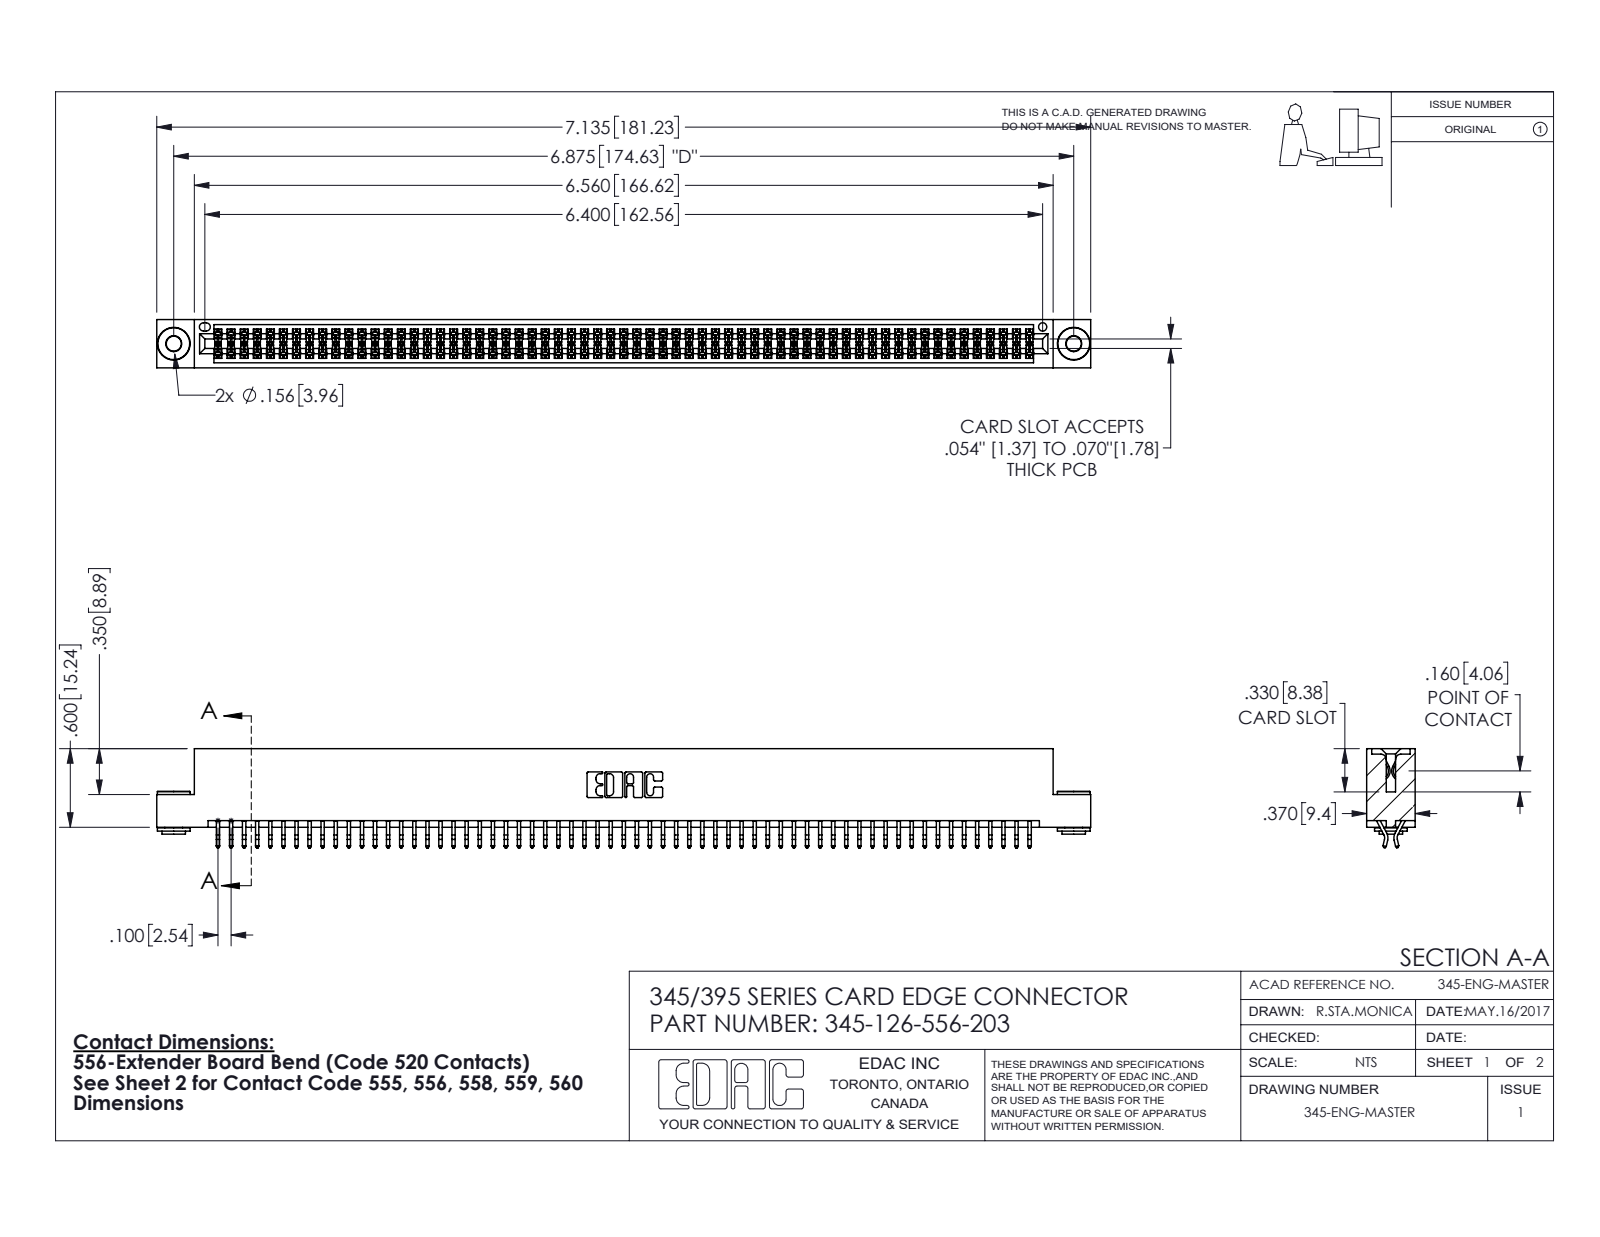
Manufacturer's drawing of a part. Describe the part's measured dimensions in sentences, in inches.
The part is named "345-250-002_345-250-002-102; 345-126-556-203; 345-292-001_556 Tail; 345 Part_Flush Mounting Lugs - 0.156 Dia-TH". Its 3-D file was written by "SolidWorks 2016 (CONFIG_CONTROL_DESIGN)". It is 129 solids with 7220 faces: 4752 planar, 2460 cylindrical and 8 other. Overall it measures 7.135 by 0.757 by 0.37 inches. Its volume is 1.087 cubic inches and its surface area 41.59 square inches. Round holes: 2 of diameter 0.116, 2 of diameter 0.156, 1 of diameter 0.064. Round bosses or shafts: 2 of diameter 0.25, 2 of diameter 0.18, 2 of diameter 0.136. Partial cylindrical surfaces (rounded edges, fillets, slot ends): 189 of radius 0.006, 22 of radius 0.01, 6 of radius 0.007, 6 of radius 0.031, 3 of radius 0.026, 2 of radius 0.01, 2 of radius 0.014, 2 of radius 0.019. The main face-to-face distances are 0.072, 0.298, 0.2, 0.37, 0.025, 0.098, 0.272, 0.225, 0.175, 0.149. The hole center spacings are 0.27, 6.639, 6.875.
